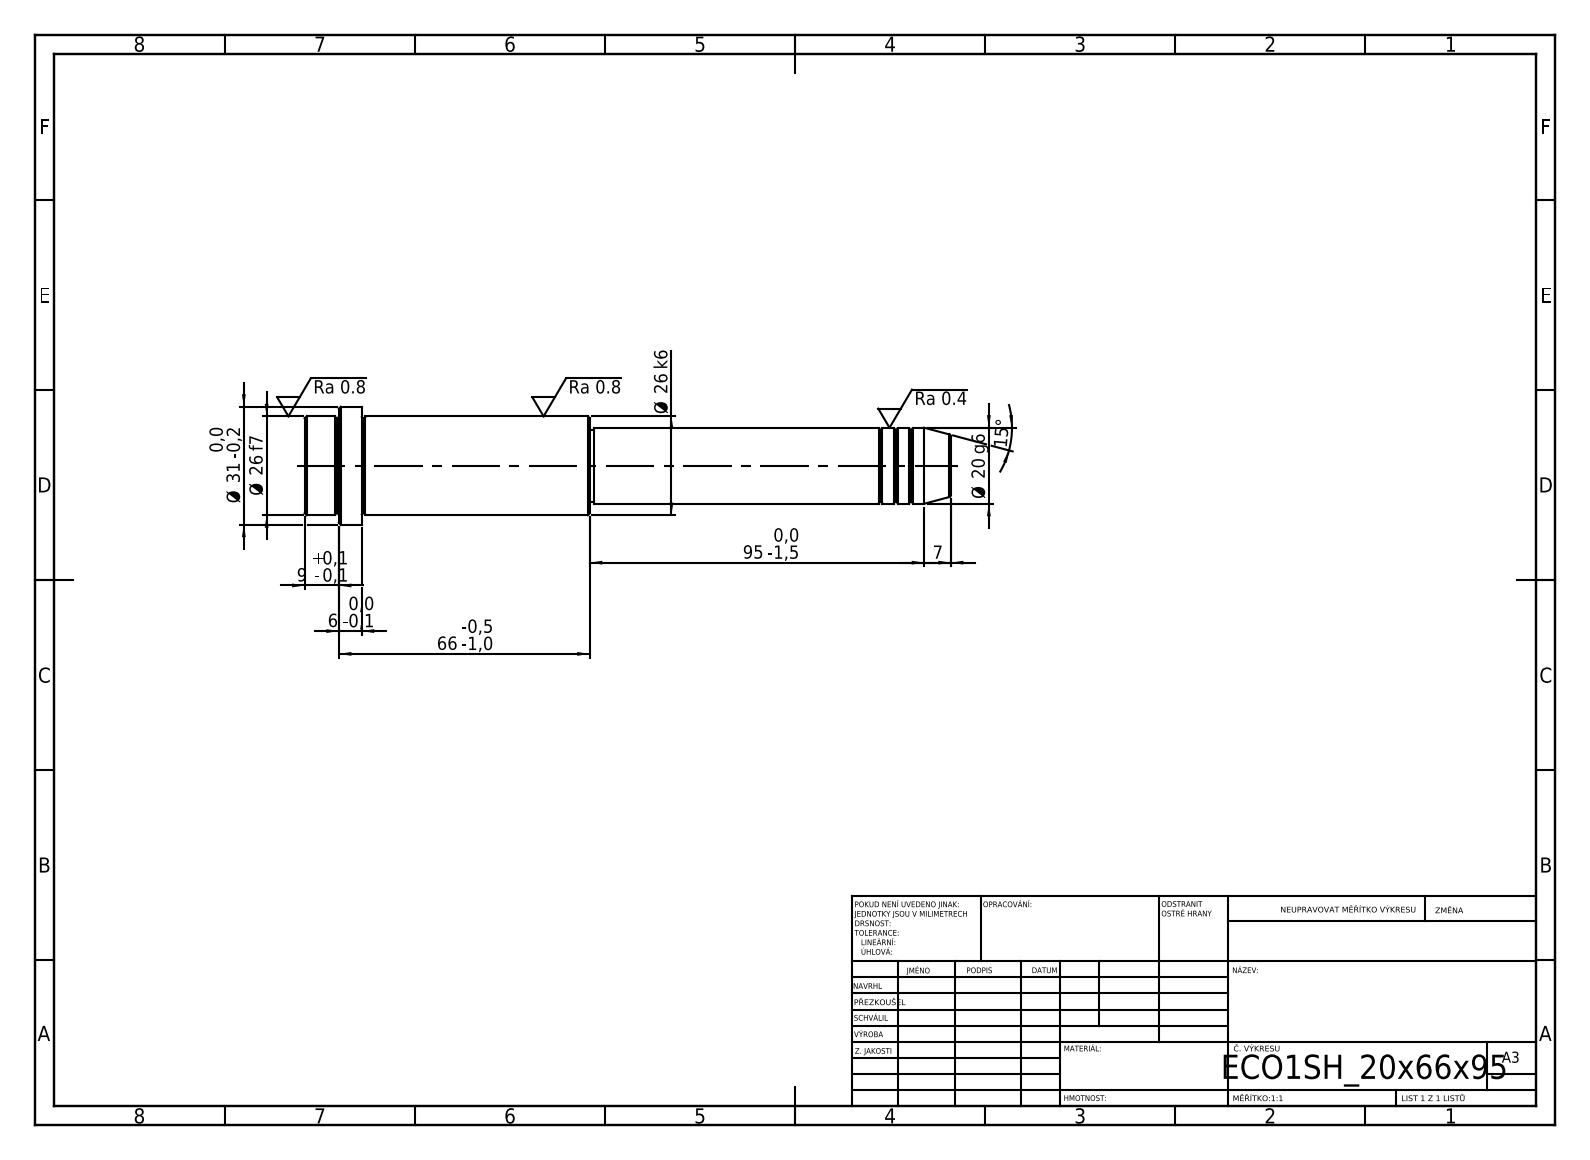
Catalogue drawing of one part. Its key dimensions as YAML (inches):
step_written_by: "SolidWorks 2019 (CONFIG_CONTROL_DESIGN)"
units: inches
bodies: {solids: 1, faces: 52, planar: 6, cylindrical: 16, other: 30}
overall_size: [6.693, 1.22, 1.22]
volume: 4.297
surface_area: 21.27
round_bosses_or_shafts:
  - {diameter: 1.22, count: 1}
  - {diameter: 1.024, count: 1}
  - {diameter: 0.787, count: 1}
  - {diameter: 0.748, count: 1}
face_to_face_distances: [0.591, 2.362, 2.953, 3.74, 6.102, 6.693, 6.339, 2.598, 0.236, 0.354]
